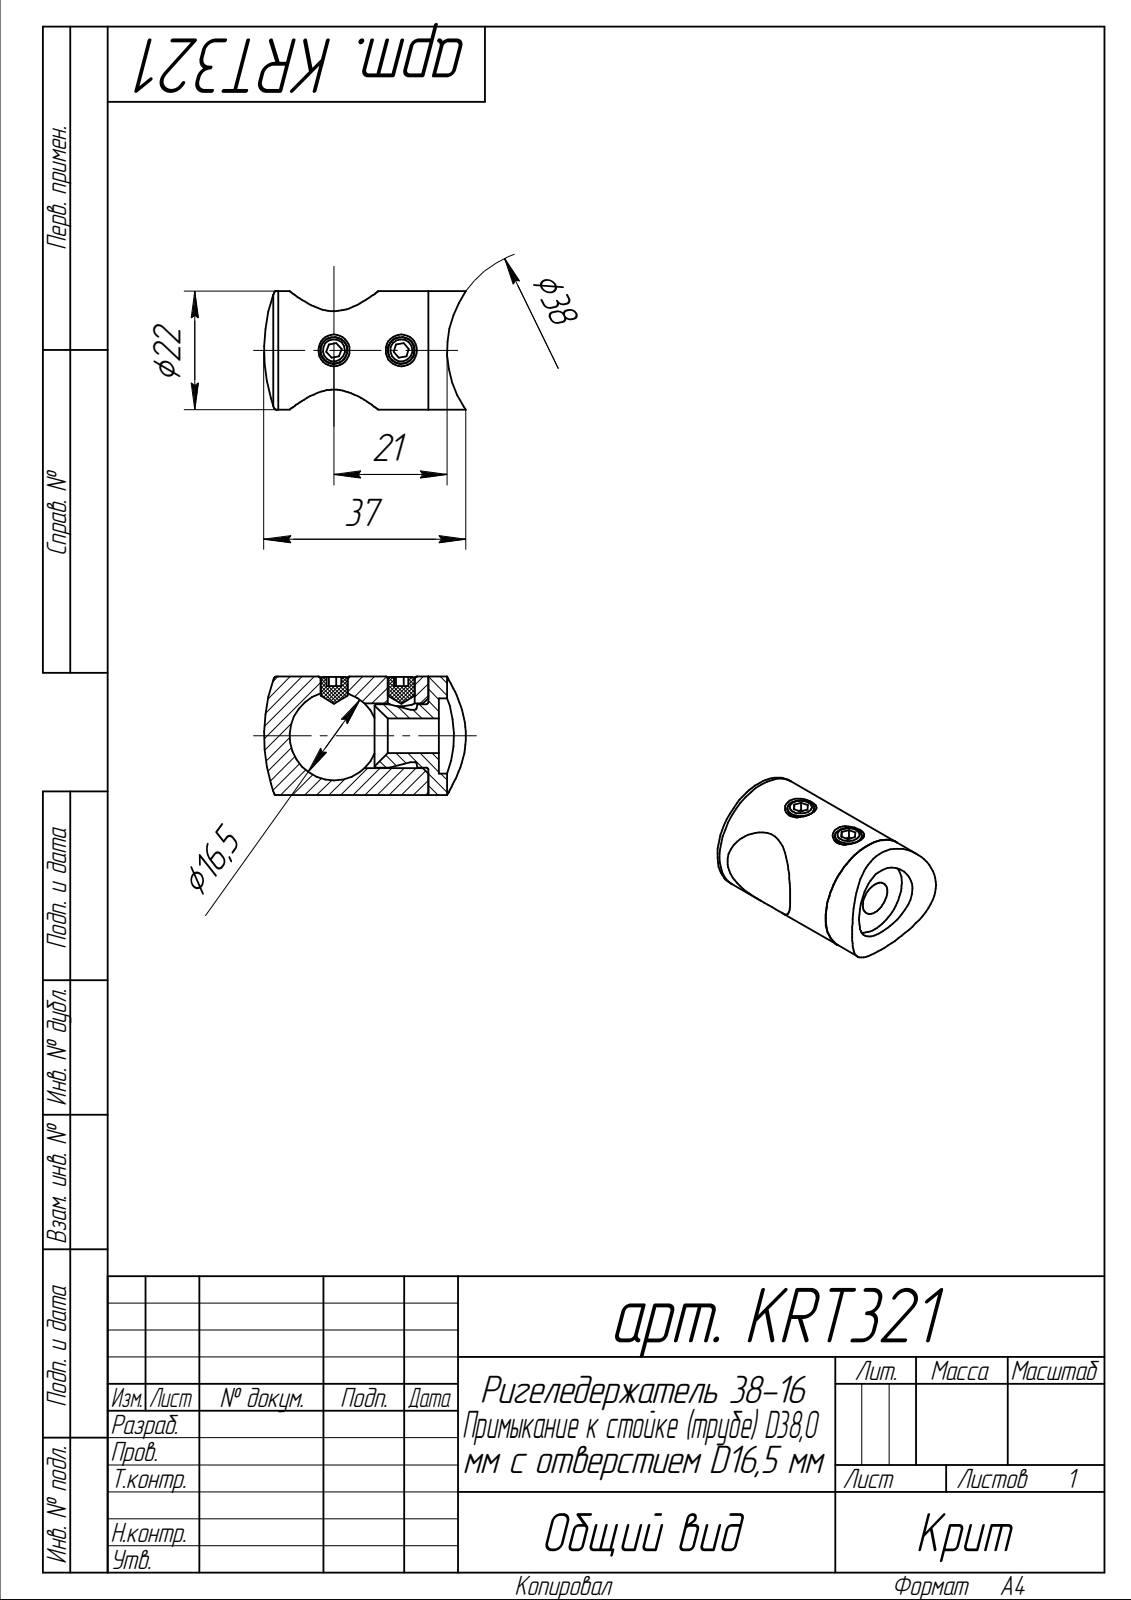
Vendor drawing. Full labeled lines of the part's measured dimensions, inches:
Part name (STEP PRODUCT): арт. KRT320.002; арт. KRT321; socket set screw cone point_am_B18.3.6M - M5 x 0.8 x 5 Hex Socket Cone Pt. SS --N; арт. KRT320.001
STEP written by: SolidWorks 2014 (AUTOMOTIVE_DESIGN)
Units: inches
Bodies: 4 solids, 78 faces (21 planar, 27 cylindrical, 30 other)
Overall size (bounding box): 1.476 × 0.866 × 0.866
Volume: 0.464 in³ · Surface area: 8.33 in²
Round holes (diameter × count): ⌀0.197 ×2, ⌀0.252 ×1, ⌀0.472 ×1, ⌀0.551 ×1, ⌀0.65 ×1
Round bosses / shafts (diameter × count): ⌀0.866 ×1, ⌀0.465 ×1, ⌀0.382 ×1
Partial cylindrical surfaces — rounded edges, fillets, slot ends (radius × count): R0.748 ×1
Main face-to-face distances: 0.079, 0.098, 0.067, 0.467, 0.099, 0.368, 0.565, 0.369, 0.198, 0.466
Hole centre spacings: 0.492
